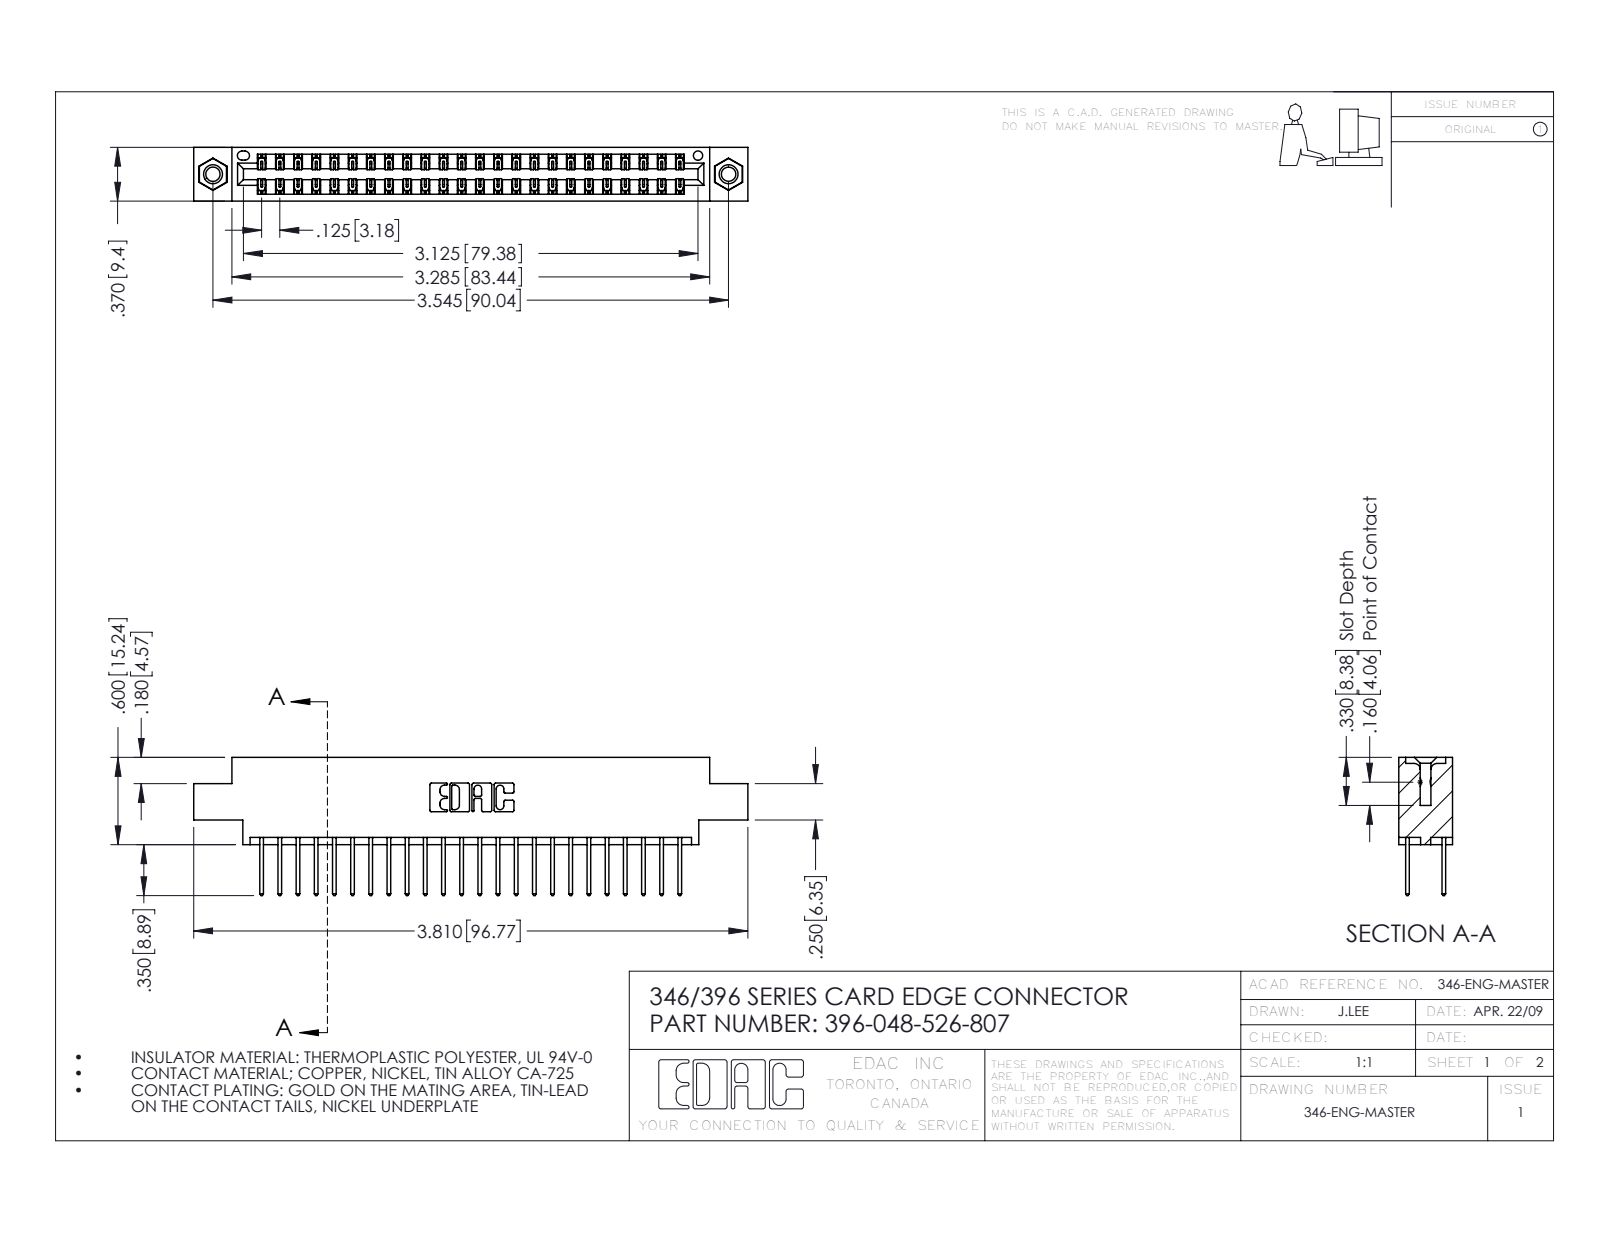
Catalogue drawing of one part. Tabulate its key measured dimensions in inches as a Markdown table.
| quantity | value |
| --- | --- |
| part name | 396-048-526-807; 345-250-001_345-250-005-103; 345-292-001_345-293-126; 346 Part_0.170 Offset - 0.156 Dia-TI |
| STEP written by | SolidWorks 2016 (CONFIG_CONTROL_DESIGN) |
| units | inches |
| bodies | 51 solids, 2682 faces (1792 planar, 874 cylindrical, 16 other) |
| overall size | 3.81 × 0.95 × 0.37 |
| volume | 0.562 in³ |
| surface area | 20.06 in² |
| round holes (diameter × count) | 0.098 × 2, 0.125 × 2, 0.156 × 2, 0.064 × 1 |
| round bosses / shafts (diameter × count) | 0.155 × 2 |
| partial cylindrical surfaces (radius × count) | 0.006 × 72, 0.01 × 48, 0.01 × 22, 0.007 × 6, 0.031 × 6, 0.026 × 3, 0.014 × 2, 0.022 × 2 |
| main face-to-face distances | 0.048, 0.322, 0.25, 0.37, 0.072, 0.298, 0.025, 0.275, 0.222, 0.148 |
| hole center spacings | 0.246, 3.337, 3.545 |
